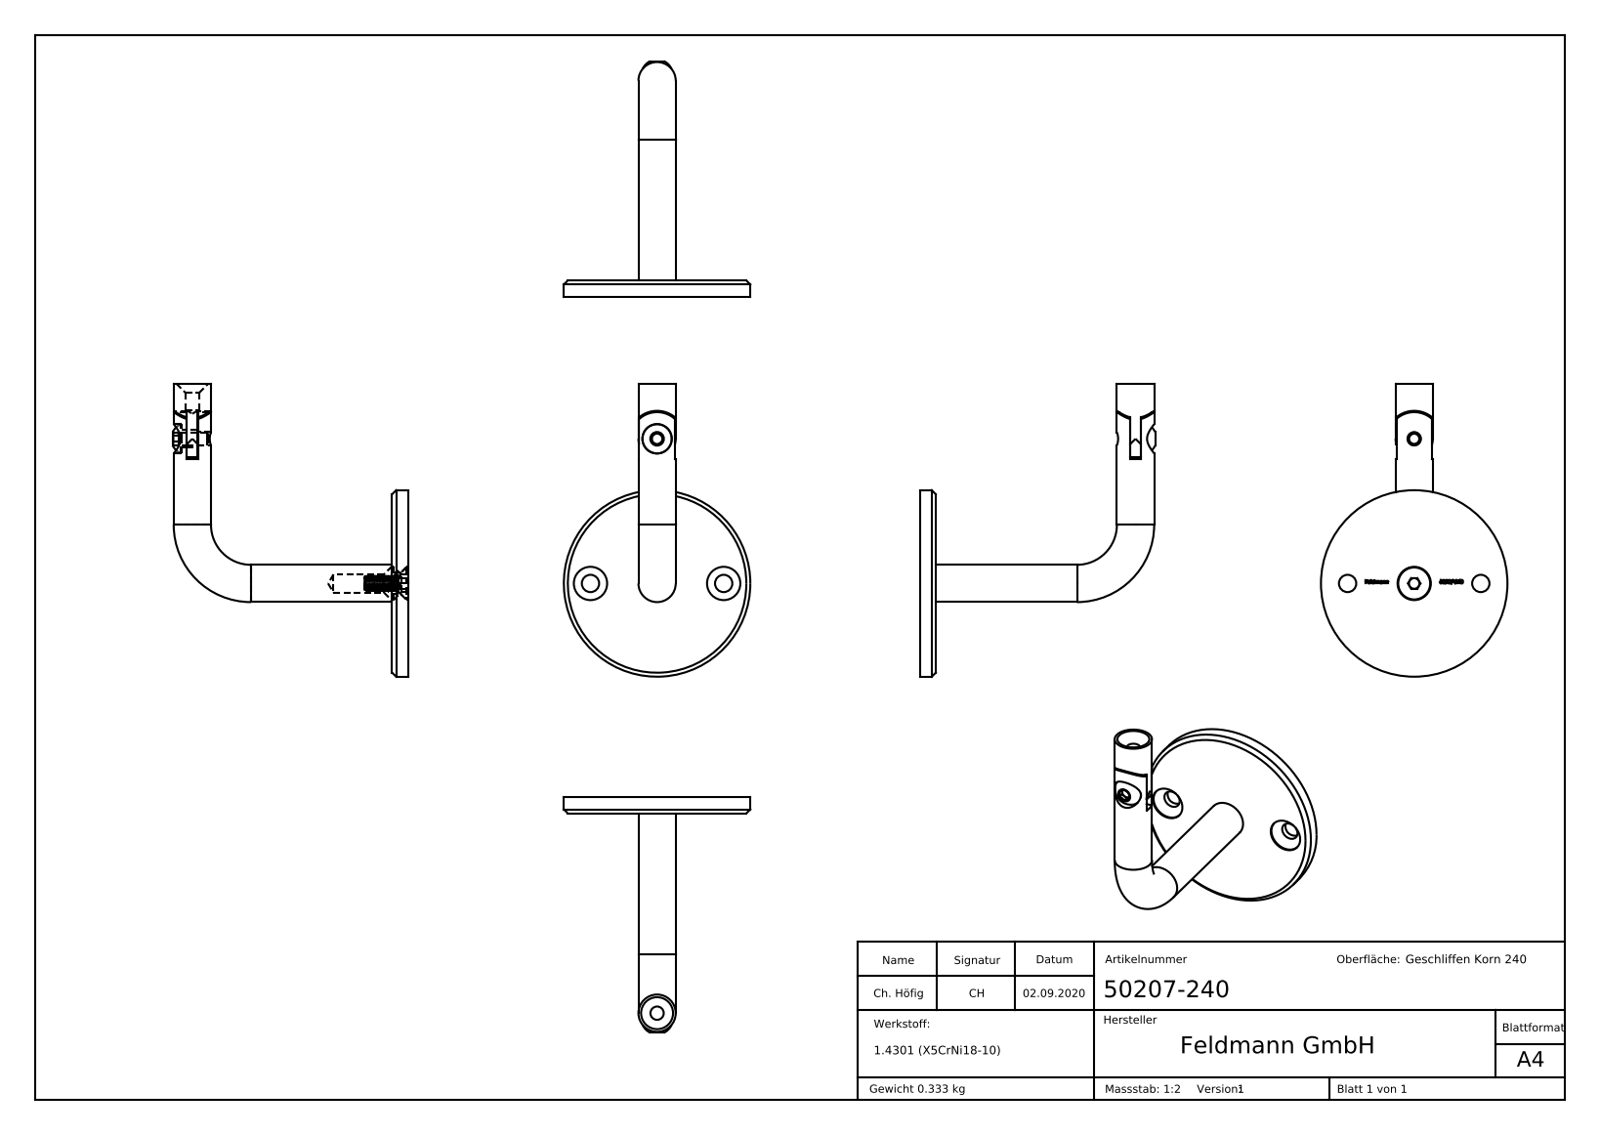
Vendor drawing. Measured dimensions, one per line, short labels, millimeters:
name: 5020X-240 Teil1_50203-240 Teil1; 5024X-240 Konfig_50244-240 Keyshot; 5024X-240 Teil2_50244-240 Teil2; 5020X-240 Teil1 (+8 more)
written by: SolidWorks 2018 (CONFIG_CONTROL_DESIGN)
unit: mm
bodies: 5 solids, 358 faces (154 planar, 68 cylindrical, 136 other)
size: 110 × 88.35 × 70
volume: 42 176 mm³; area: 18 304 mm²
holes: 3× ⌀6.5, 3× ⌀12.5, 2× ⌀5, 1× ⌀6.8, 1× ⌀8, 1× ⌀11
bosses: 2× ⌀14, 1× ⌀70, 1× ⌀12, 1× ⌀6, 1× ⌀4.77
rounds: 1× R7, 1× R10, 1× R10.5
face distances: 6, 4.05, 4, 78.95, 72.95, 83.05, 77.05, 4.1, 77, 73
hole spacings: 25, 59.78, 50, 54.3
